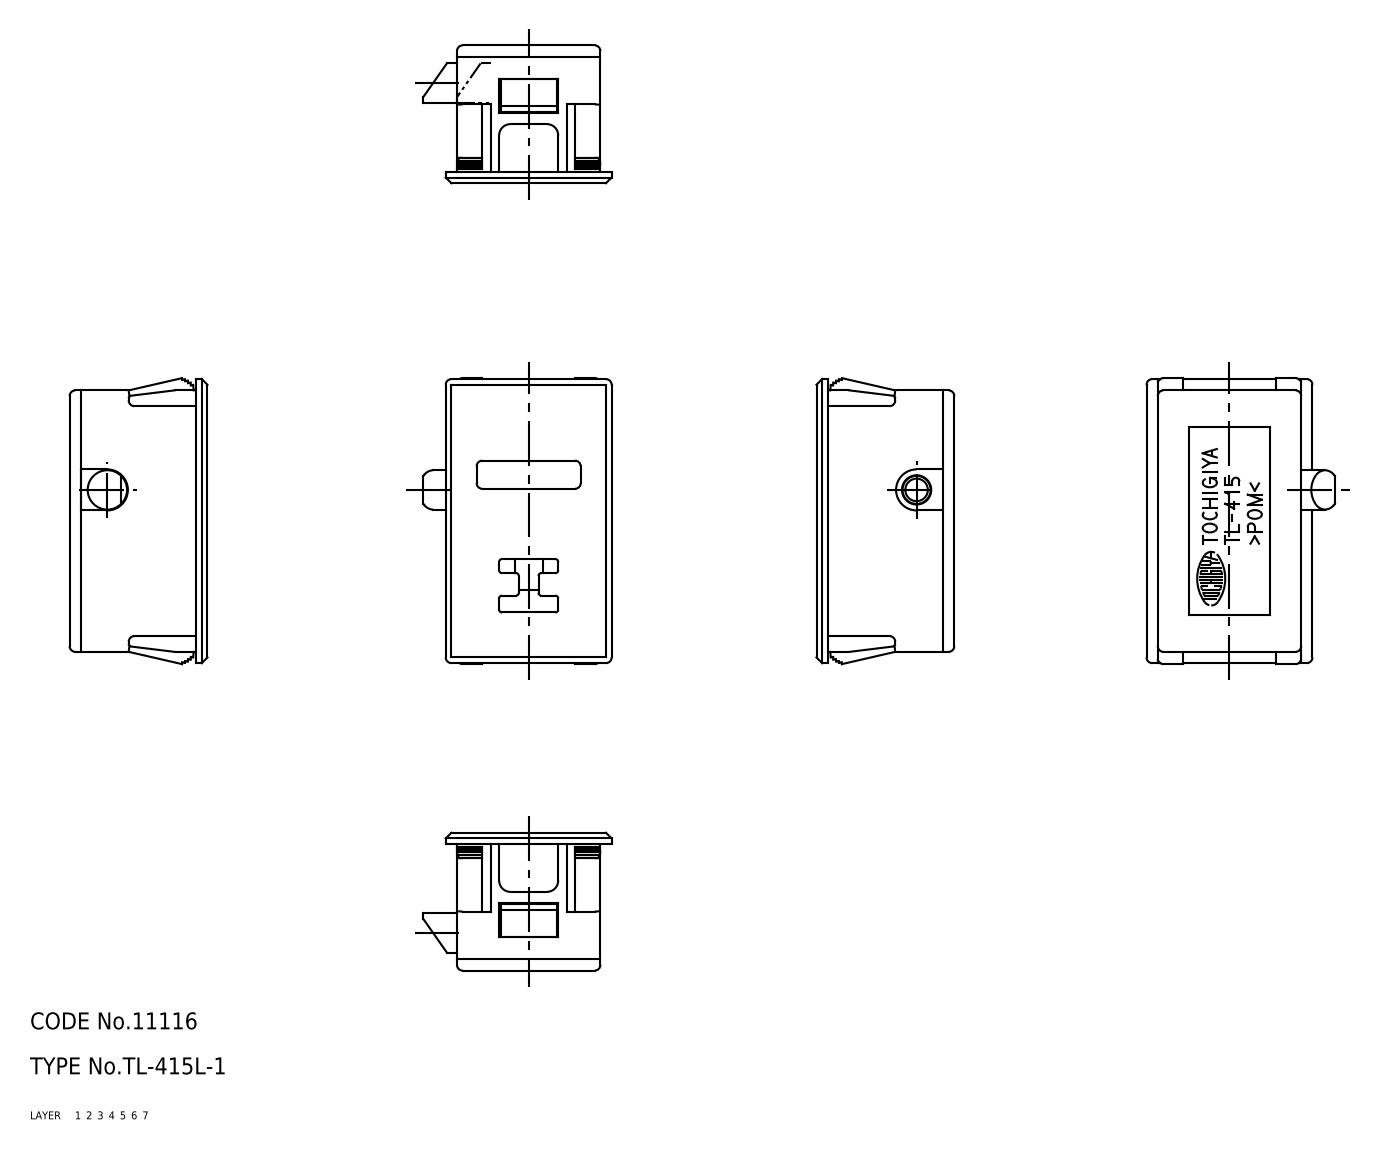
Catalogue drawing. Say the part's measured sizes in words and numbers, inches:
The part is named "TL_415L_1; latch". Its 3-D file was written by "SolidWorks 2015 (AUTOMOTIVE_DESIGN)". It is 1 solid with 213 faces: 135 planar, 62 cylindrical and 16 other. Overall it measures 2.002 by 1.319 by 0.965 inches. Its volume is 1.726 cubic inches and its surface area 11.98 square inches. Round bosses or shafts: 1 of diameter 0.276. Partial cylindrical surfaces (rounded edges, fillets, slot ends): 26 of radius 0.02, 22 of radius 0.039, 2 of radius 0.079, 2 of radius 0.118, 1 of radius 0.144. The main face-to-face distances are 0.079, 0.965, 1.004, 0.886, 1.831, 0.11, 1.72, 0.787, 0.295, 1.752.
